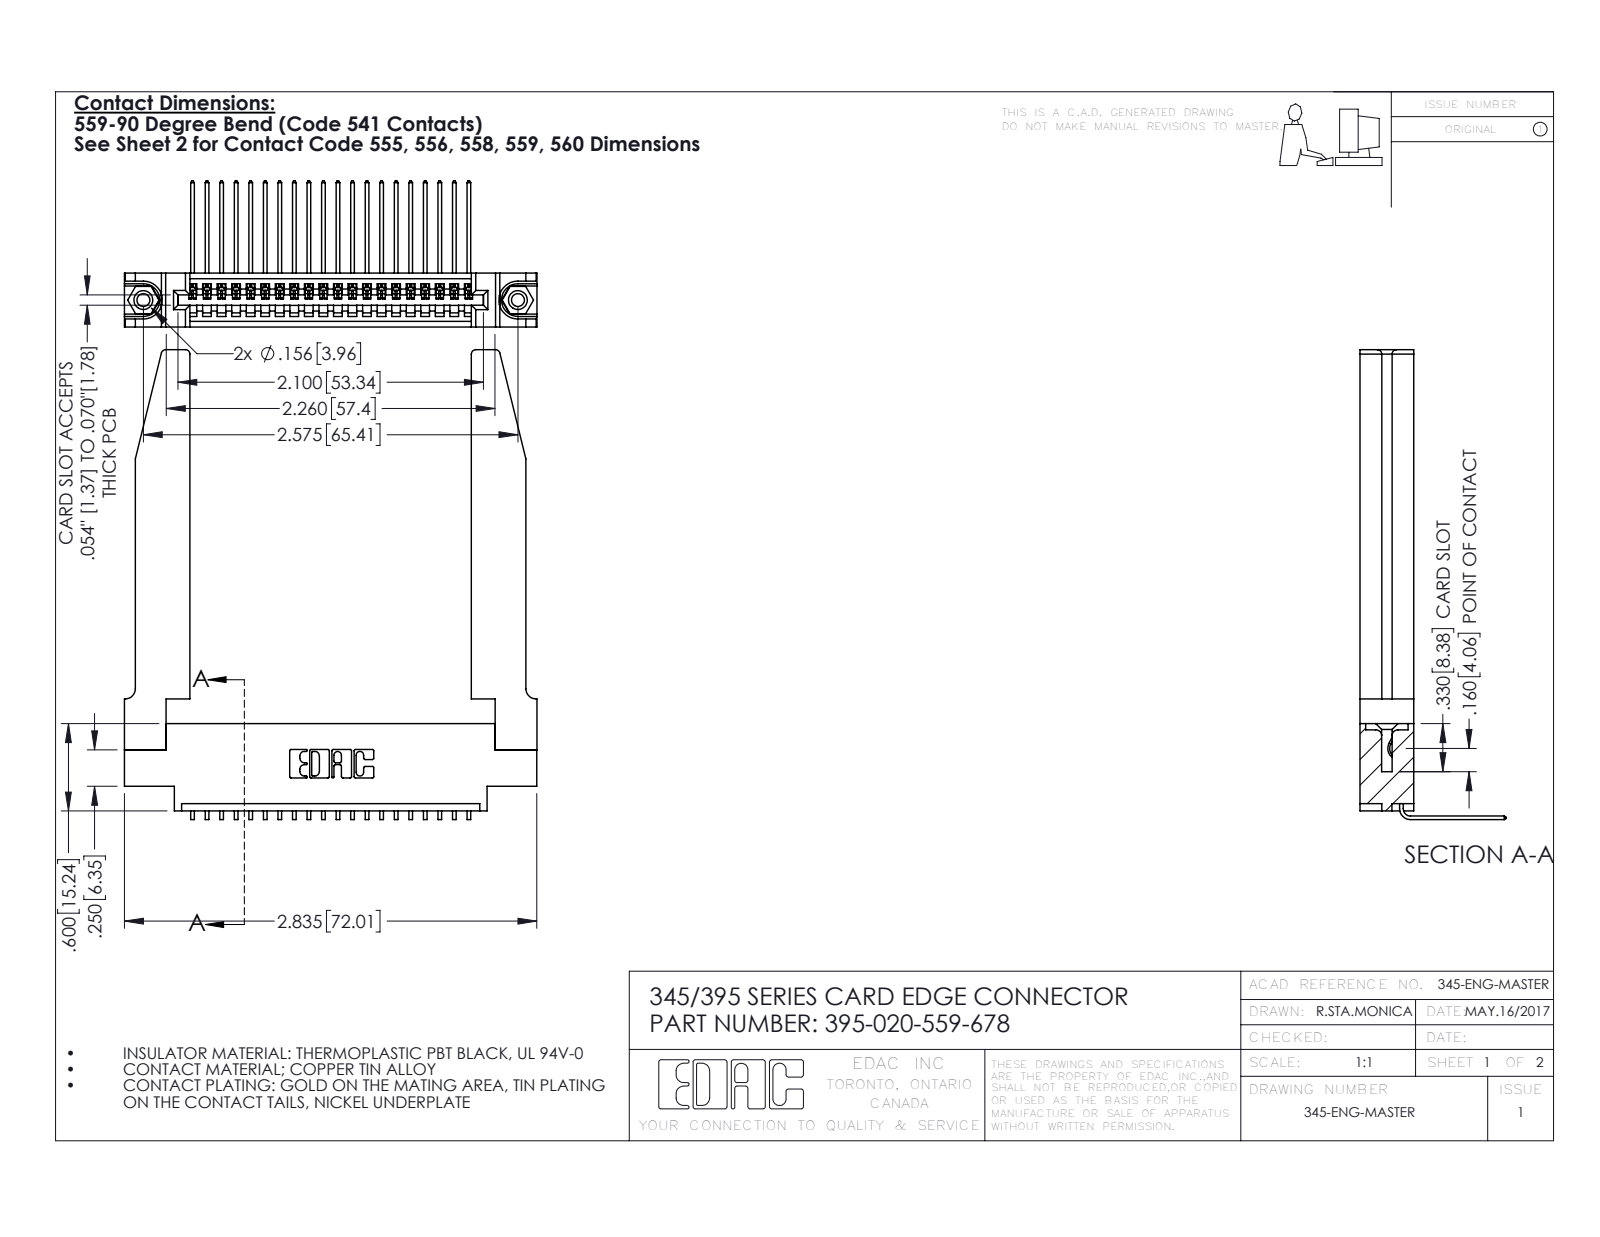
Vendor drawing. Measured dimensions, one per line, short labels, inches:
name: 345-220-078_345-220-078; 345-292-001_558 559 Tail - 1; 395-020-559-678; 345-250-001_345-250-001-102 (+1 more)
written by: SolidWorks 2016 (CONFIG_CONTROL_DESIGN)
unit: in
bodies: 25 solids, 1564 faces (1066 planar, 446 cylindrical, 52 other)
size: 3.229 × 2.836 × 1.005
volume: 0.878 in³; area: 24.58 in²
holes: 2× ⌀0.089, 2× ⌀0.125, 2× ⌀0.156, 1× ⌀0.064
bosses: 2× ⌀0.155
rounds: 40× R0.006, 22× R0.01, 8× R0.03, 6× R0.007, 6× R0.031, 3× R0.026, 2× R0.031, 2× R0.04
face distances: 0.37, 0.072, 0.298, 0.148, 0.15, 0.098, 0.272, 0.025, 0.2, 0.22
hole spacings: 0.27, 2.341, 2.575
